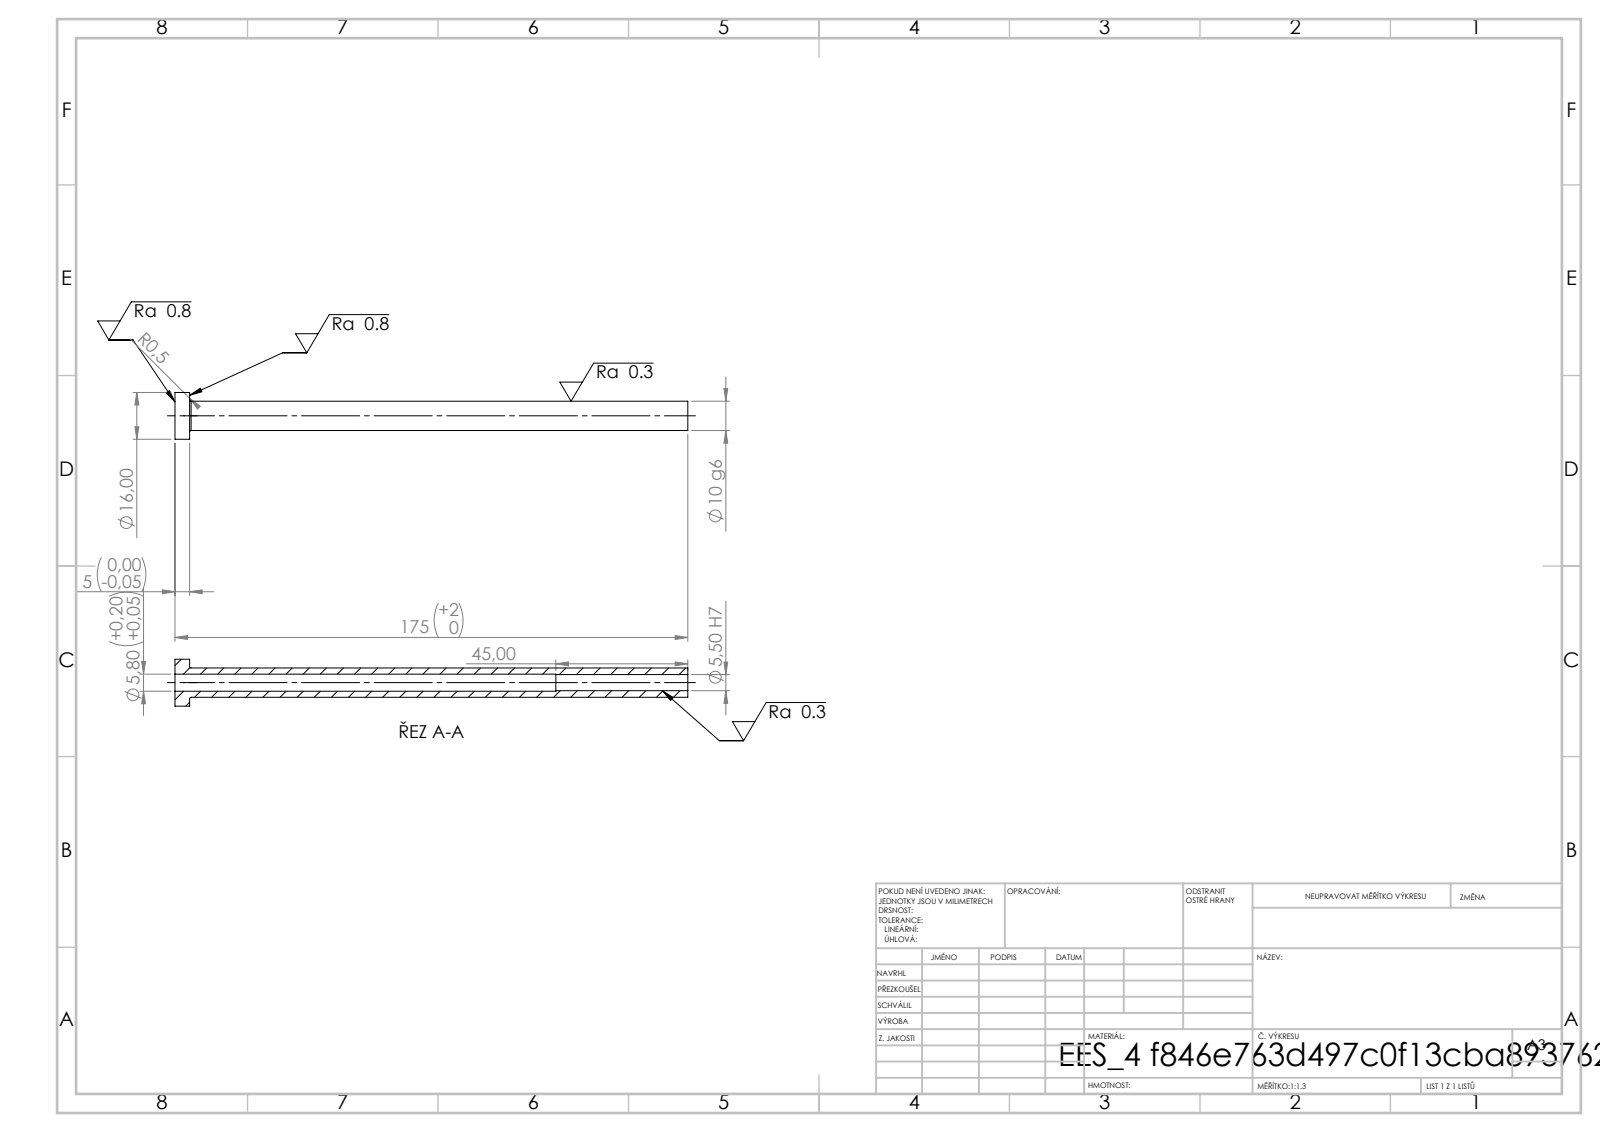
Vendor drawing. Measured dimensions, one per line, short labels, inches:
written by: SolidWorks 2019 (CONFIG_CONTROL_DESIGN)
unit: in
bodies: 1 solid, 14 faces (4 planar, 8 cylindrical, 2 other)
size: 6.89 × 0.63 × 0.63
volume: 0.601 in³; area: 14.08 in²
holes: 1× ⌀0.217, 1× ⌀0.228
bosses: 1× ⌀0.63, 1× ⌀0.394
face distances: 0.197, 6.89, 6.693, 5.118, 4.921, 1.772
